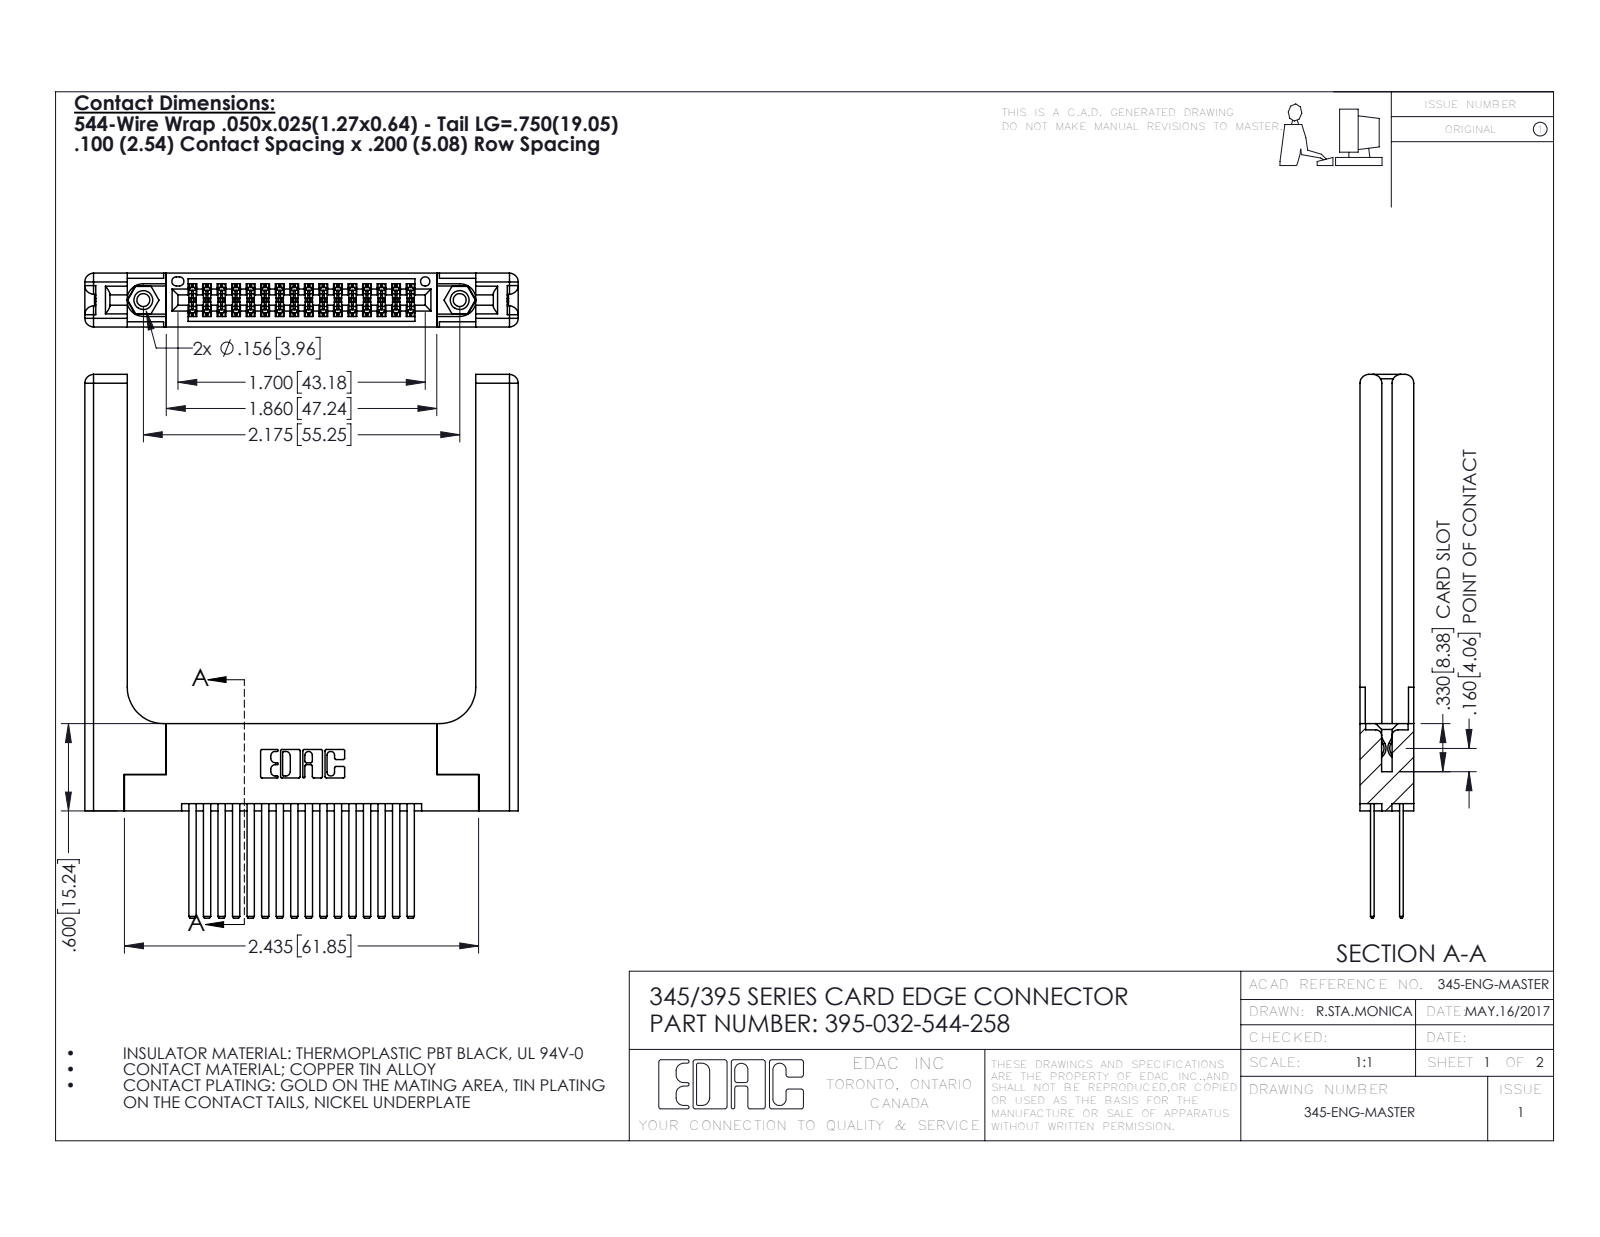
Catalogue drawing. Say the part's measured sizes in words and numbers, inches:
The part is named "345 Part_Flush Mounting Lugs - 0.156 Dia-TH; 345-250-001_345-250-001-102; 345-292-001_345-293-144; 345-220-058_345-220-058 (+1 more)". Its 3-D file was written by "SolidWorks 2016 (CONFIG_CONTROL_DESIGN)". It is 37 solids with 1790 faces: 1156 planar, 574 cylindrical and 60 other. Overall it measures 3.737 by 2.979 by 0.37 inches. Its volume is 0.978 cubic inches and its surface area 26.41 square inches. Round holes: 2 of diameter 0.089, 2 of diameter 0.125, 2 of diameter 0.156, 1 of diameter 0.064. Round bosses or shafts: 2 of diameter 0.155. Partial cylindrical surfaces (rounded edges, fillets, slot ends): 48 of radius 0.006, 22 of radius 0.01, 16 of radius 0.06, 6 of radius 0.007, 6 of radius 0.031, 3 of radius 0.026, 2 of radius 0.014, 2 of radius 0.019. The main face-to-face distances are 0.072, 0.298, 0.37, 0.2, 0.098, 0.272, 0.025, 0.225, 0.077, 0.15. The hole center spacings are 0.27, 1.942, 2.175.
